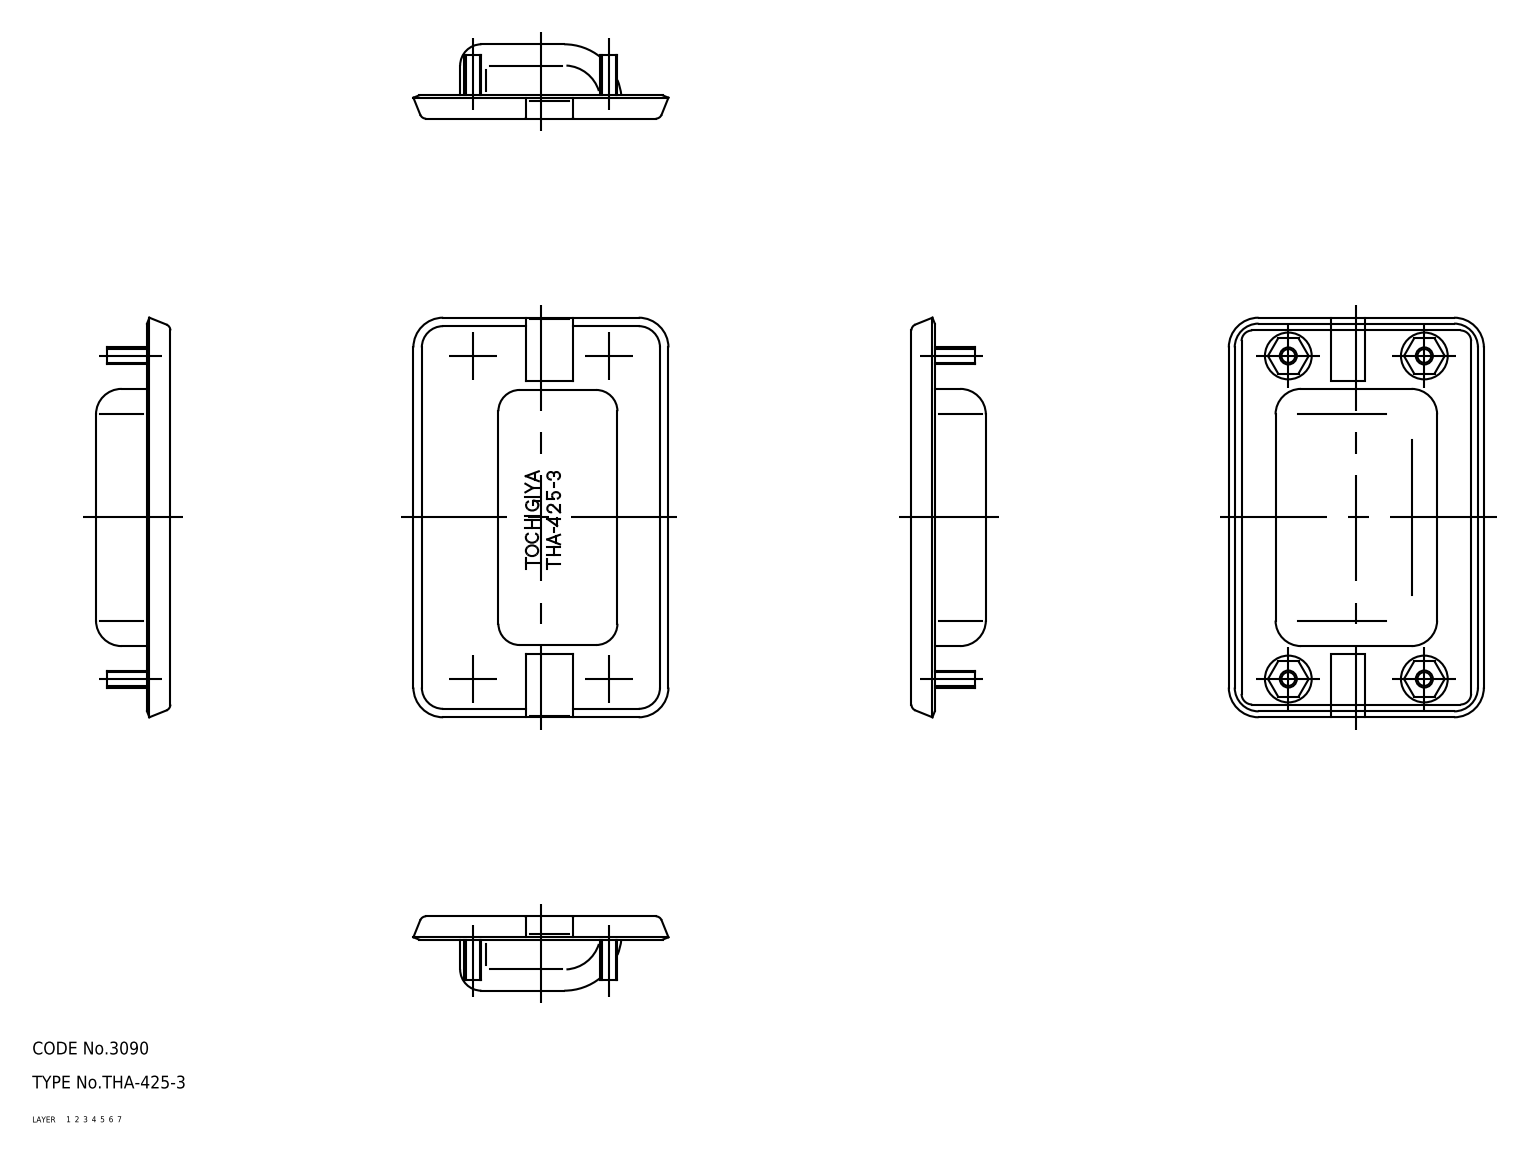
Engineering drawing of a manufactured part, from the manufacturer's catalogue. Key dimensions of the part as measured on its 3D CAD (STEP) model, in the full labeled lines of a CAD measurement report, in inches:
Part name (STEP PRODUCT): bolt; cover; base; THA_425_3_28996_36
STEP written by: CADfix (AUTOMOTIVE_DESIGN)
Units: inches
Bodies: 6 solids, 422 faces (0 planar, 0 cylindrical, 422 other)
Overall size (bounding box): 3.701 × 2.362 × 0.689
Volume: 0.703 in³ · Surface area: 39.67 in²
